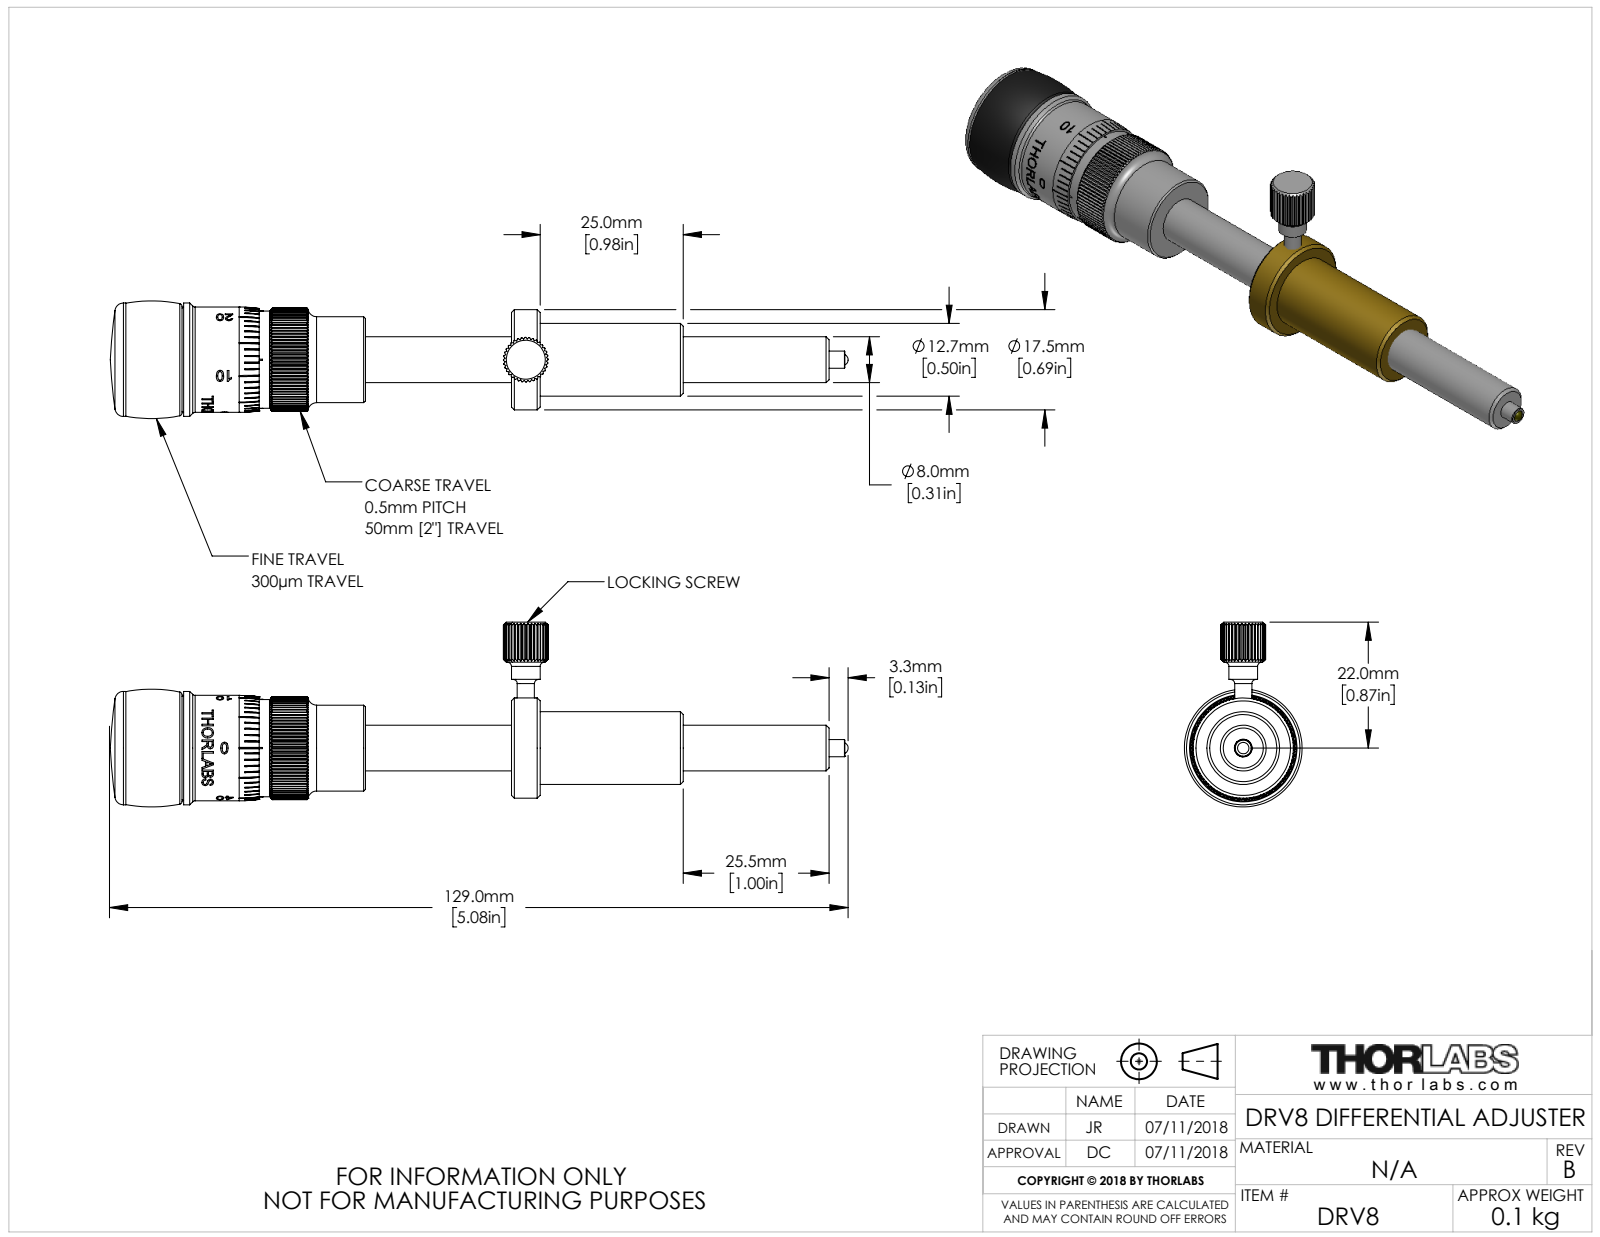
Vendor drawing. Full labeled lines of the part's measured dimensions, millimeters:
Part name (STEP PRODUCT): 136351 - DRV8 Drive Rod; 136349 - DRV8 Mounting Sleeve; 136350 - DRV8 M8 Drive Screw; 131028 DRV3 4mm Hard Pad (+8 more)
STEP written by: SolidWorks 2009 (AUTOMOTIVE_DESIGN)
Units: millimetres
Bodies: 31 solids, 1418 faces (565 planar, 341 cylindrical, 512 other)
Overall size (bounding box): 128.62 × 31.66 × 20.55
Volume: 17 703 mm³ · Surface area: 17 357 mm²
Round holes (diameter × count): ⌀1.6 ×4, ⌀1 ×3, ⌀1.25 ×3, ⌀2 ×1, ⌀2.5 ×1, ⌀3 ×1, ⌀3.1 ×1, ⌀4.3 ×1, ⌀4.5 ×1, ⌀5 ×1, ⌀5.5 ×1, ⌀7.5 ×1
Round bosses / shafts (diameter × count): ⌀1.5 ×4, ⌀3 ×2, ⌀1 ×2, ⌀19.8 ×1, ⌀18.4 ×1, ⌀17.5 ×1, ⌀17 ×1, ⌀15.6 ×1
Partial cylindrical surfaces — rounded edges, fillets, slot ends (radius × count): R0.5 ×14, R1.1 ×1, R3.9 ×1, R8.25 ×1, R8.51 ×1, R9 ×1
Main face-to-face distances: 25.5, 50.85, 25.35, 15.95, 35.62, 10.12, 15.23, 63.05, 37.55, 27.43
Hole centre spacings: 9.5, 9.6, 19.1, 24.91, 45.15, 54.65, 64.25
